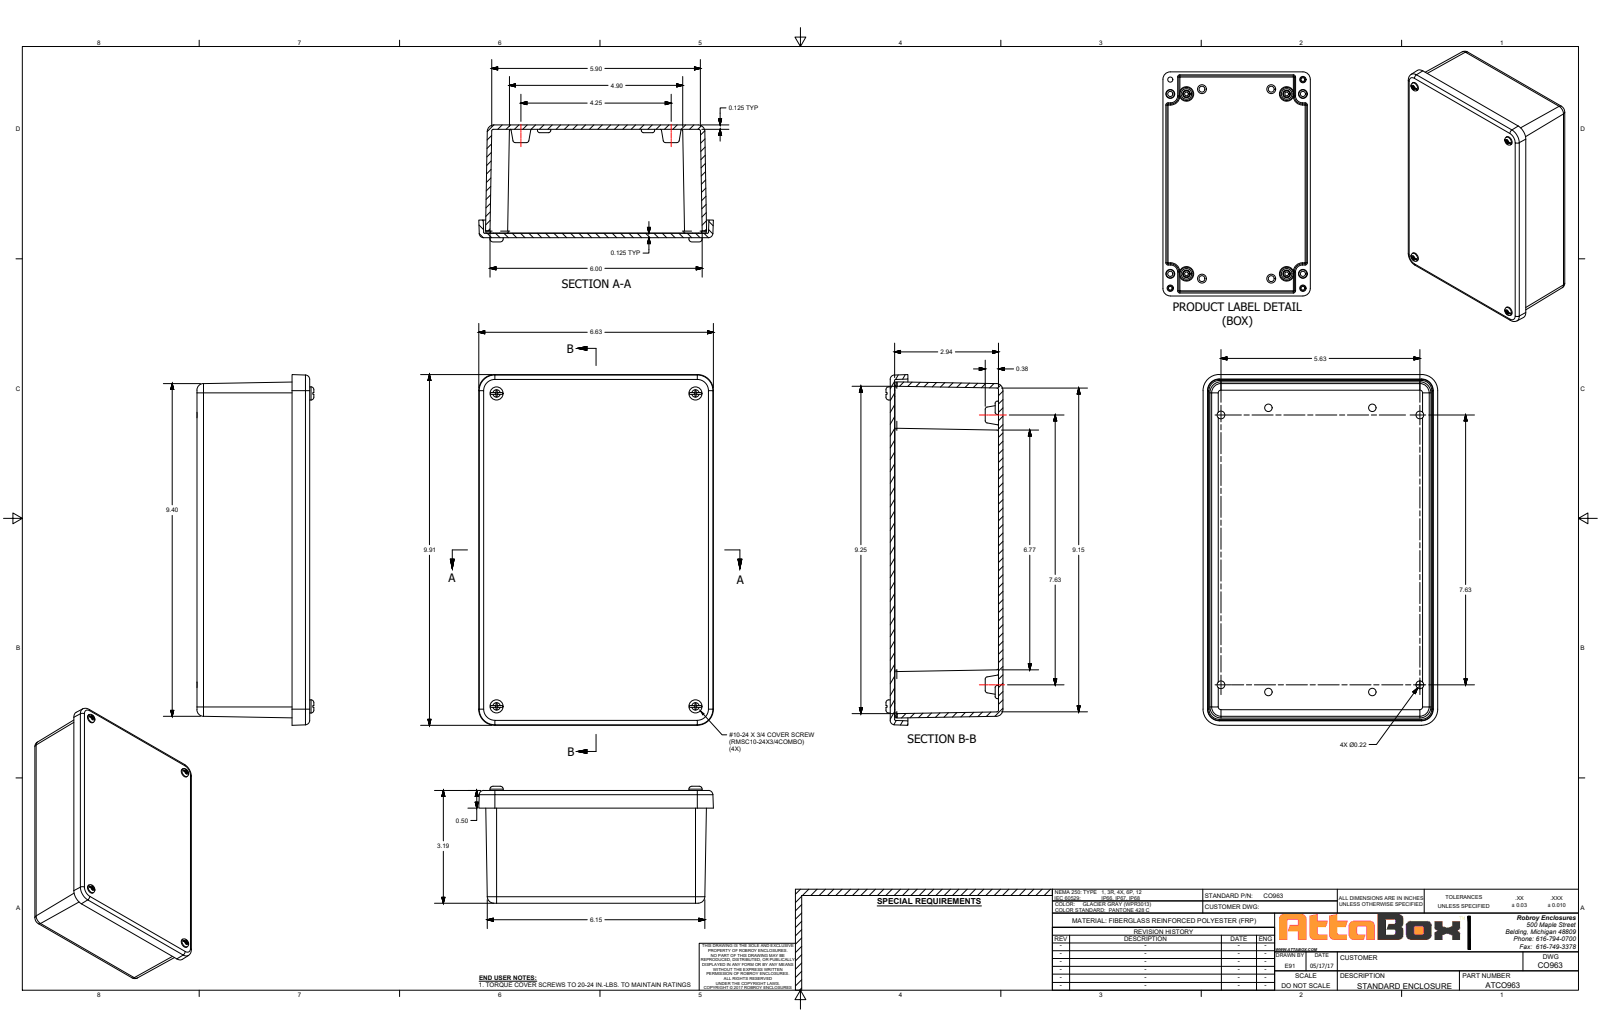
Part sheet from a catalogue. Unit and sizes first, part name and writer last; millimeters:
Units: millimetres
Overall size (bounding box): 251.7 × 168.5 × 84
Round holes (diameter × count): ⌀4 ×8, ⌀5.6 ×8, ⌀5.3 ×4, ⌀6.4 ×4, ⌀7.1 ×4
Round bosses / shafts (diameter × count): ⌀6.9 ×8, ⌀9.5 ×4, ⌀9.4 ×4, ⌀4.5 ×4
Partial cylindrical surfaces — rounded edges, fillets, slot ends (radius × count): R0.8 ×20, R0.3 ×16, R1.1 ×8, R3.2 ×4, R4.7 ×4
Main face-to-face distances: 3.2, 3.2, 77.8, 80.9, 74.6, 77.8, 12.7, 15.9, 1.6, 4.7
Hole centre spacings: 15.5, 17.4, 17.5, 23.3, 34.5, 35.7, 91.4, 108.9
Volume: 549 500 mm³ · Surface area: 310 500 mm²
Bodies: 15 solids, 356 faces (148 planar, 112 cylindrical, 96 other)
Part name (STEP PRODUCT): CO963
STEP written by: SolidWorks 2018 (AUTOMOTIVE_DESIGN)
